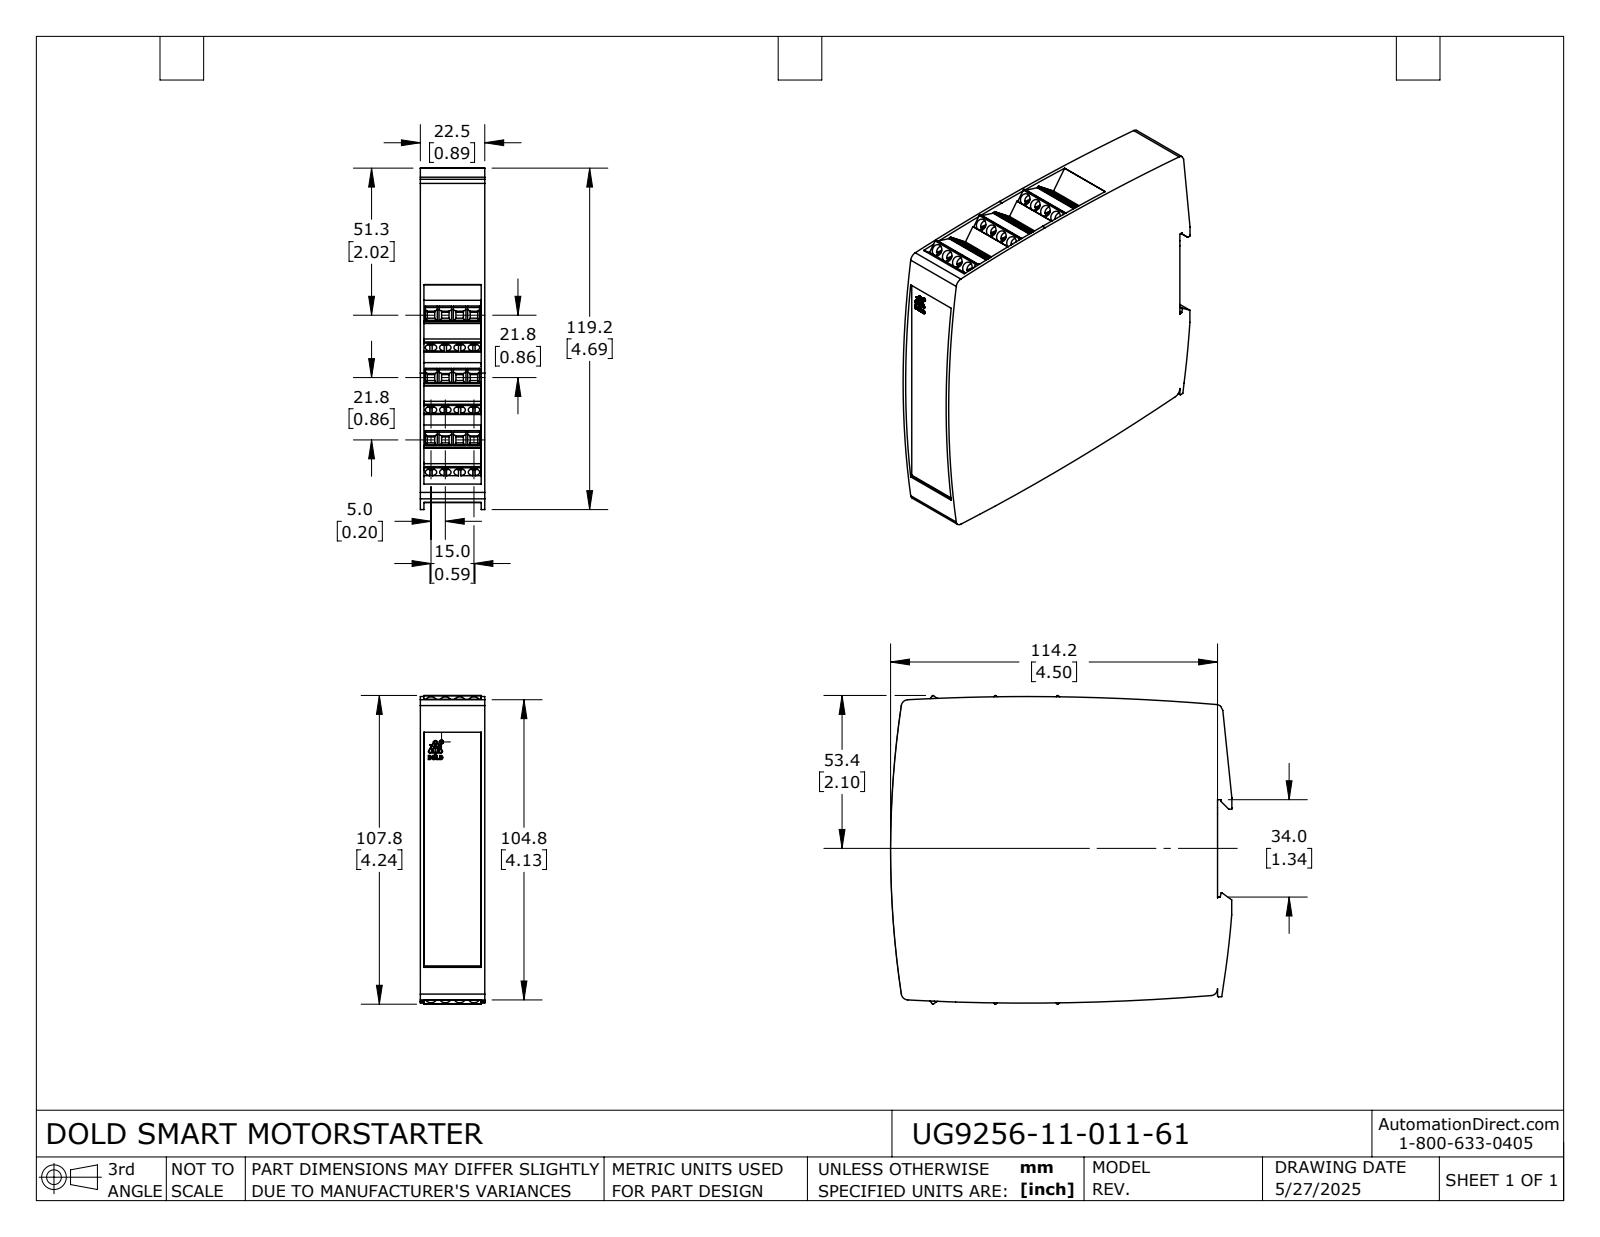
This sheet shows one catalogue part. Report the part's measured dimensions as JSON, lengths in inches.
{"part_name": "UG9256-11-011-61", "step_written_by": "SolidWorks 2024 (AUTOMOTIVE_DESIGN)", "units": "inches", "bodies": {"solids": 1, "faces": 1036, "planar": 813, "cylindrical": 222, "other": 1}, "overall_size": [4.693, 4.243, 0.886], "volume_in3": 15.85, "surface_area_in2": 64.72, "round_holes": [[0.157, 24], [0.053, 1]], "round_bosses_or_shafts": [[0.15, 24], [0.049, 1]], "partial_cylinders_radius": [[0.012, 15], [0.02, 14], [0.004, 12], [0.094, 7], [0.005, 6], [0.004, 4], [31.496, 4], [0.021, 3]], "face_to_face_distances": [0.886, 0.049, 0.837, 0.675, 4.379, 0.051, 0.835, 1.35, 0.528, 0.785], "hole_center_spacings": [0.563, 0.197, 0.528, 0.658, 0.394, 1.073, 0.792, 1.055]}
